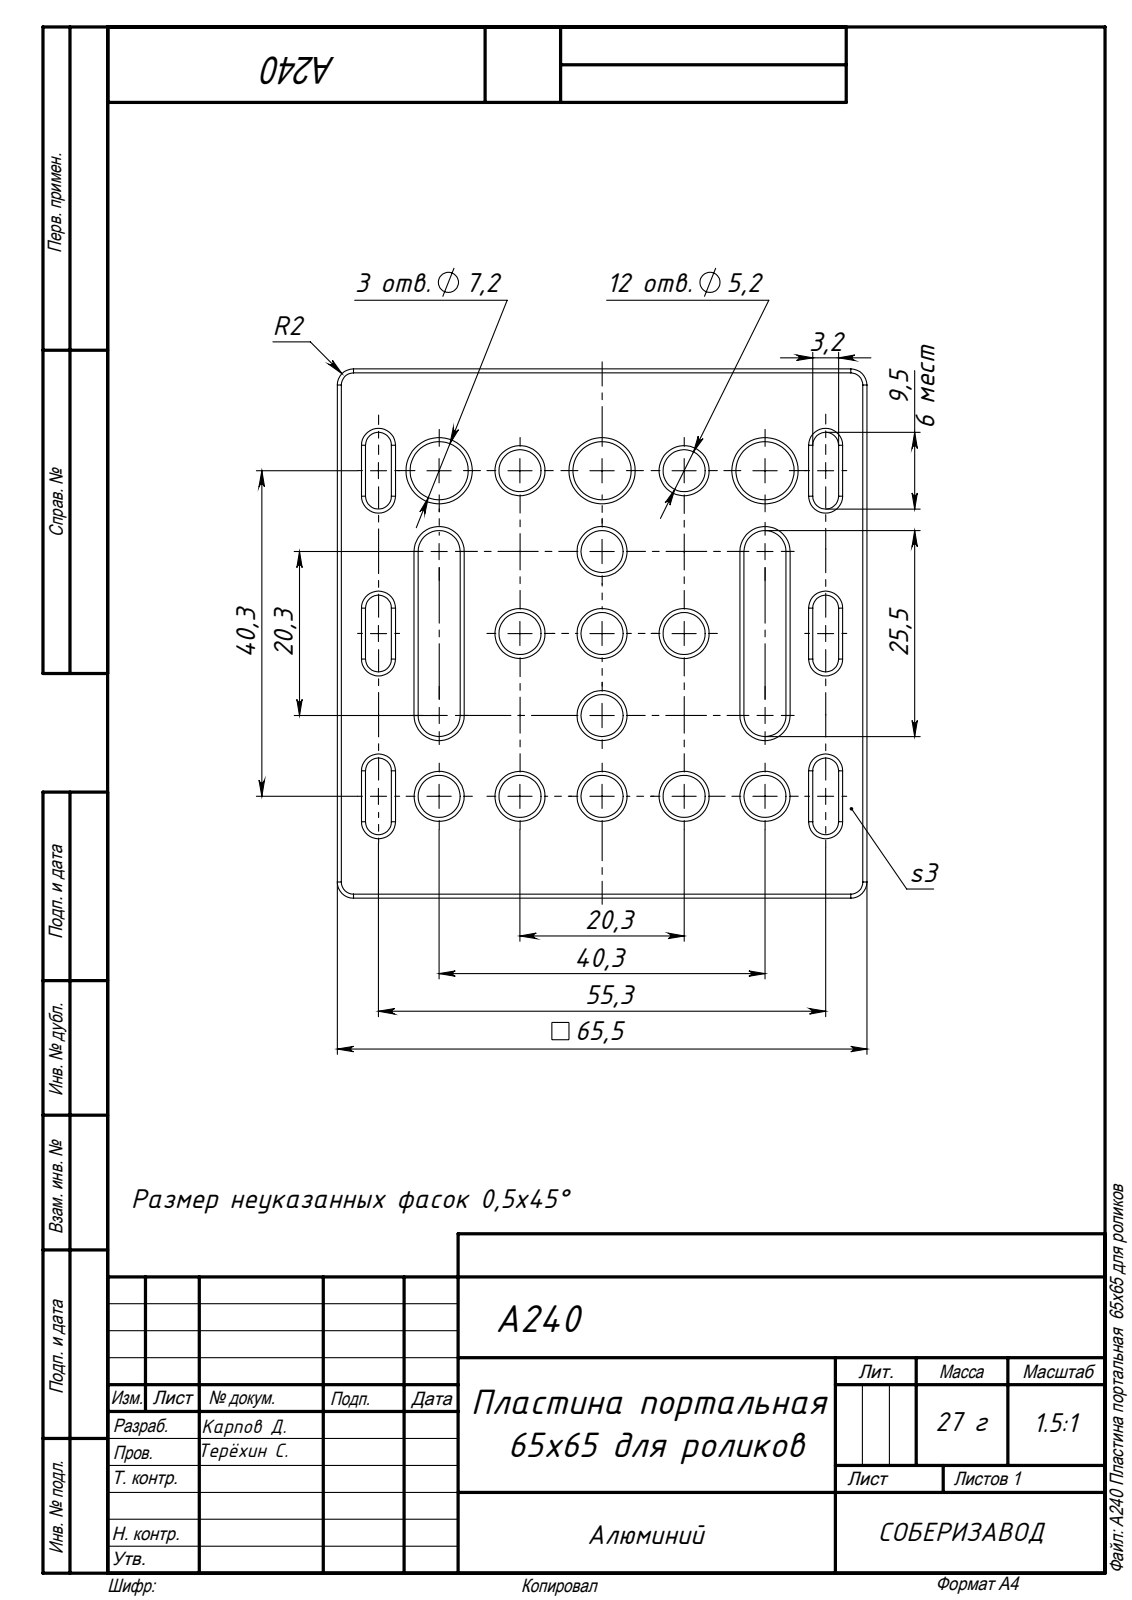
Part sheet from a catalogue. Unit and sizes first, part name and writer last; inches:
Units: inches
Overall size (bounding box): 2.579 × 2.579 × 0.118
Round holes (diameter × count): ⌀0.205 ×12, ⌀0.283 ×3
Partial cylindrical surfaces — rounded edges, fillets, slot ends (radius × count): R0.063 ×12, R0.079 ×4, R0.102 ×4
Main face-to-face distances: 0.118, 2.579, 0.394, 0.598, 1.98, 2.185, 0.205, 1.587, 0.138, 0.264
Hole centre spacings: 0.793, 0.4, 0.885, 0.888, 1.433, 1.587, 0.394, 1.193
Volume: 0.631 in³ · Surface area: 13.96 in²
Bodies: 1 solid, 172 faces (42 planar, 50 cylindrical, 80 other)
Part name (STEP PRODUCT): A240 Пластина портальная 65х65 для роликов
STEP written by: SolidWorks 2018 (AUTOMOTIVE_DESIGN)
